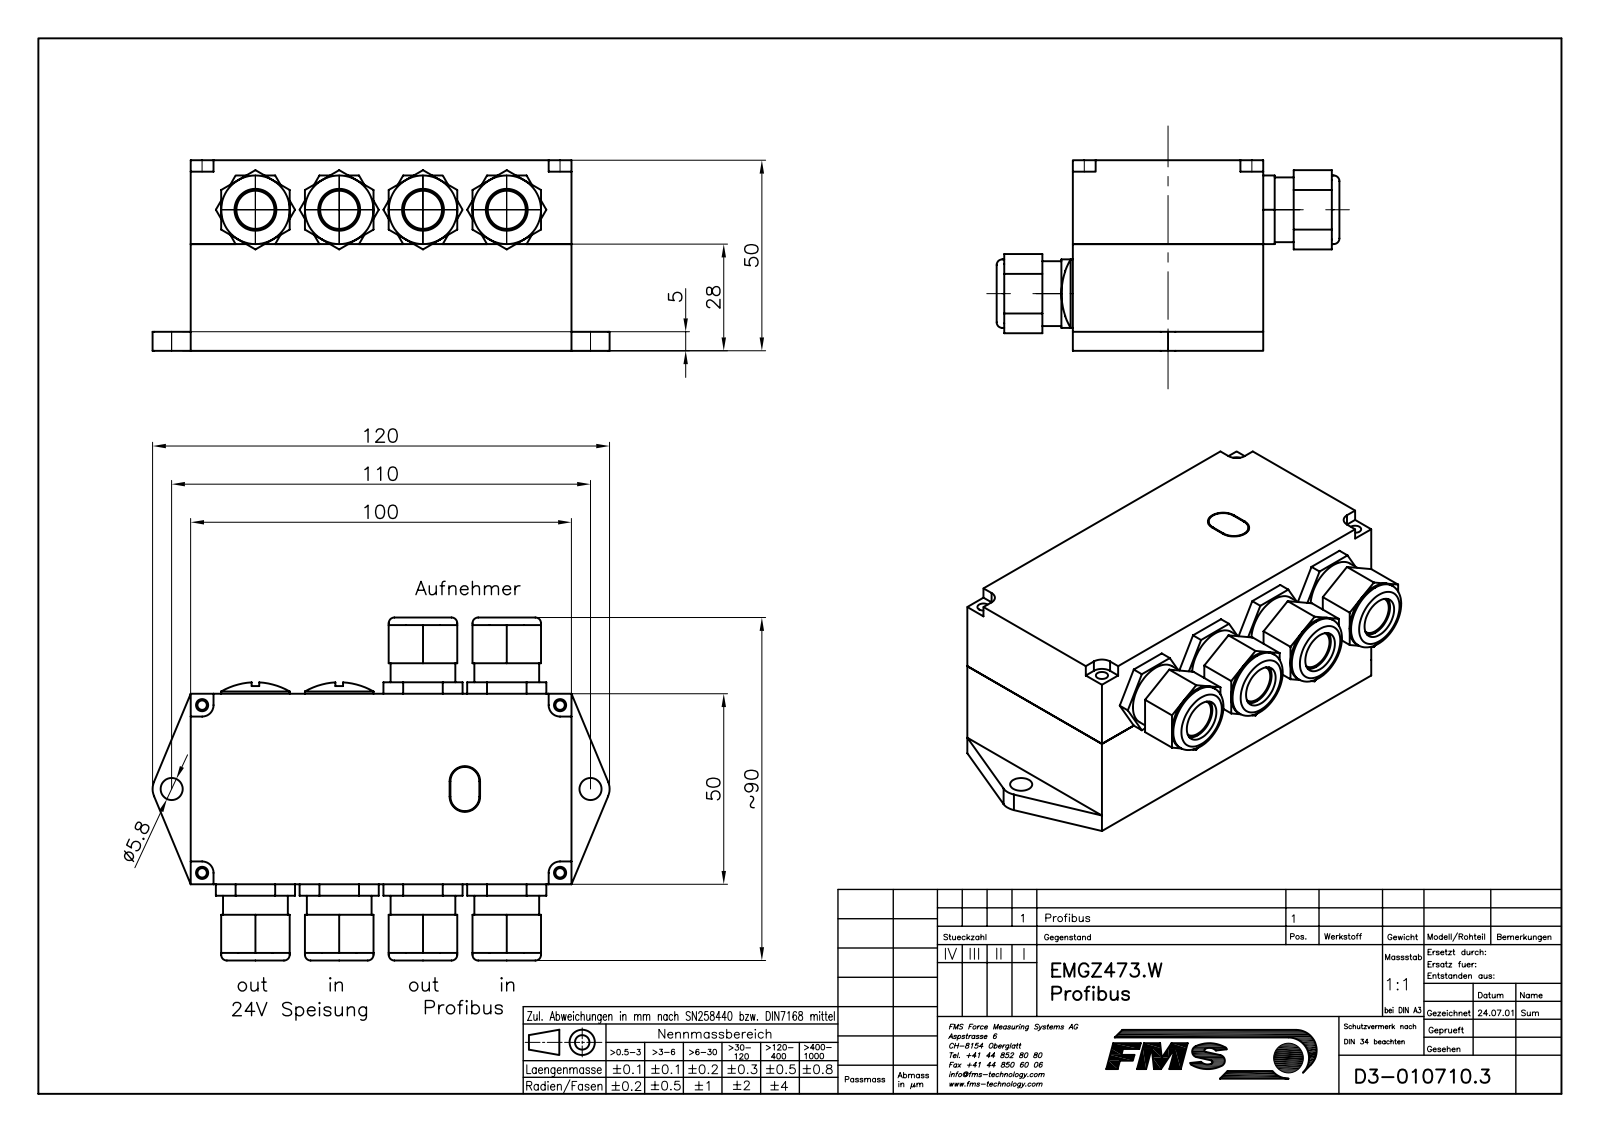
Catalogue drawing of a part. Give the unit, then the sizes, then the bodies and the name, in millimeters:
Units: millimetres
Overall size (bounding box): 120 × 90 × 50
Round holes (diameter × count): ⌀13.9 ×8, ⌀10 ×6, ⌀11 ×6, ⌀12 ×6, ⌀13.5 ×6, ⌀16.15 ×6, ⌀2 ×4, ⌀2.46 ×4, ⌀3.2 ×4, ⌀5.8 ×2, ⌀12.2 ×2
Round bosses / shafts (diameter × count): ⌀18 ×8, ⌀17 ×6, ⌀16 ×6, ⌀15.5 ×6, ⌀15.2 ×2, ⌀3 ×1
Partial cylindrical surfaces — rounded edges, fillets, slot ends (radius × count): R5 ×26, R3 ×6, R1 ×4, R3.7 ×4, R3.8 ×2, R4 ×2
Main face-to-face distances: 50, 4, 44, 22, 18, 48, 26, 2, 46, 6
Hole centre spacings: 22, 31.11, 44, 8.9, 20.18, 23.41, 37.41, 49.19
Volume: 118 547 mm³ · Surface area: 81 625 mm²
Bodies: 23 solids, 606 faces (274 planar, 240 cylindrical, 92 other)
Part name (STEP PRODUCT): E0107103; E0107107; KABELVERSCHRAUBUNG_M16X1.5; TEIL1 (+8 more)
STEP written by: Mechanical Desktop 2009 (CONFIG_CONTROL_DESIGN)
